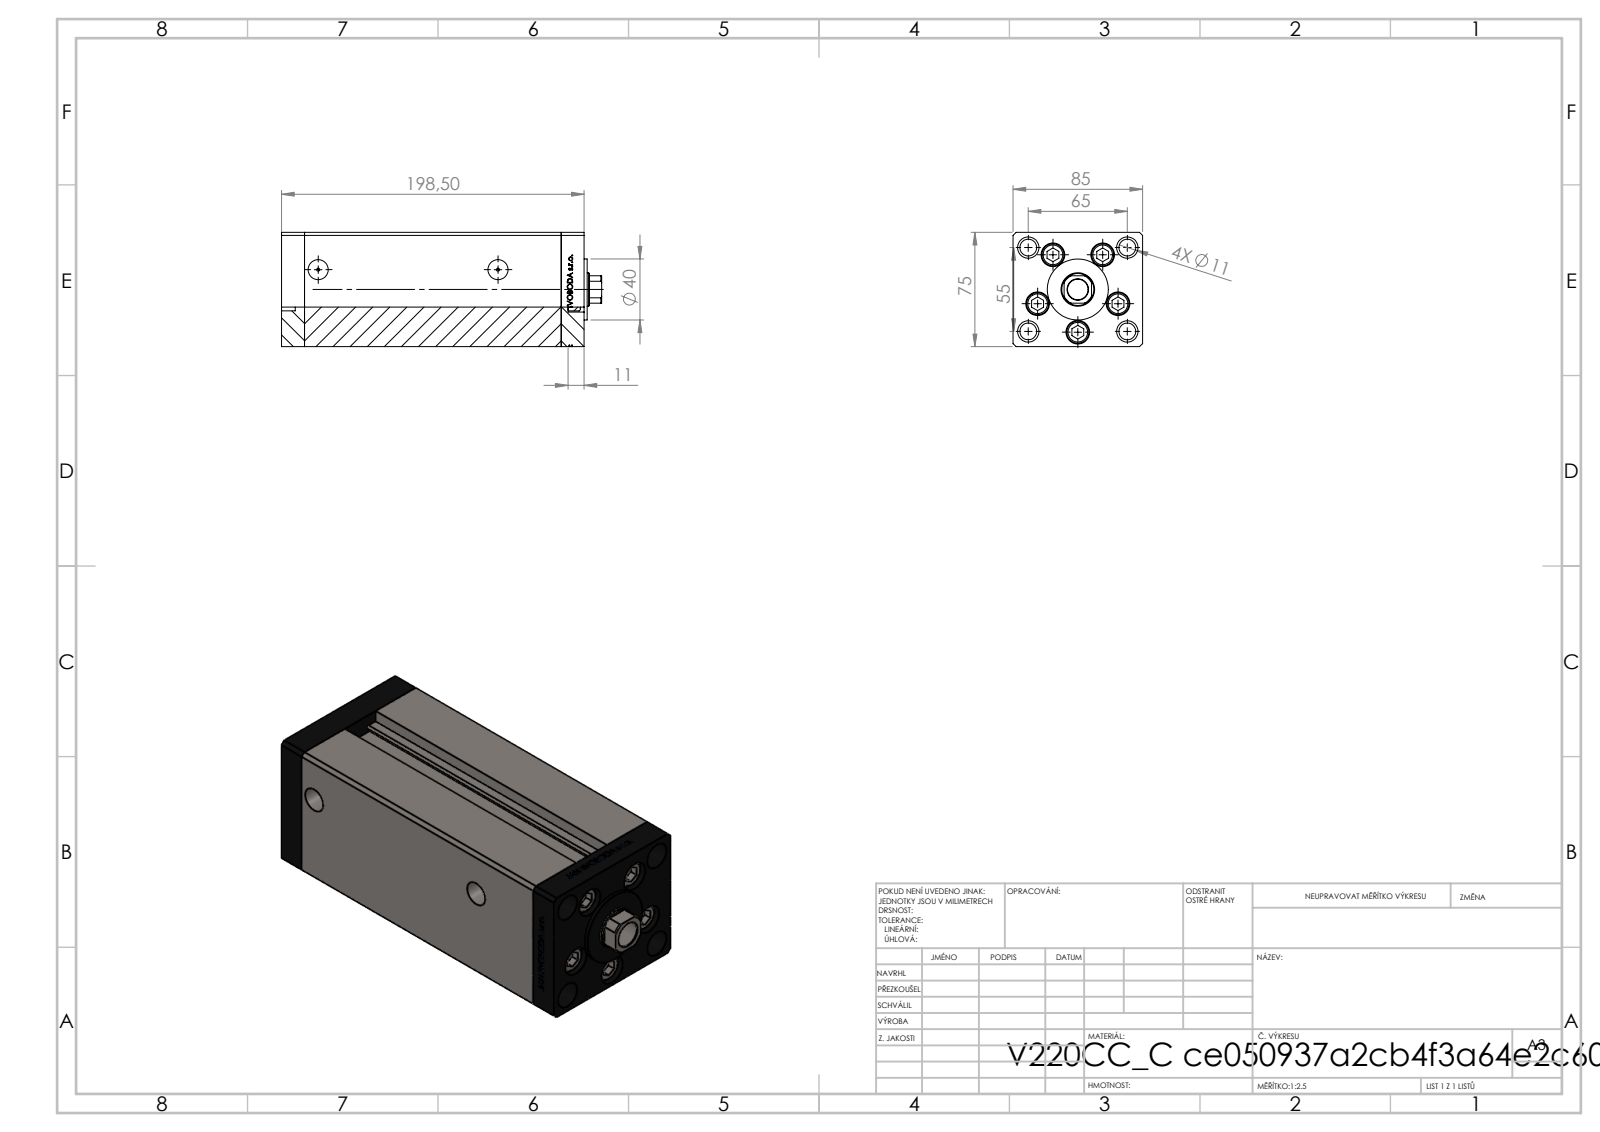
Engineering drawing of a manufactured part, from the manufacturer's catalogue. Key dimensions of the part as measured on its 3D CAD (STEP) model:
Part name (STEP PRODUCT): V220C FRONT; V220C_VC_C; V220C_C MIDDLE; V220C BACK_C (+1 more)
STEP written by: SolidWorks 2019 (CONFIG_CONTROL_DESIGN)
Units: millimetres
Bodies: 13 solids, 1175 faces (546 planar, 167 cylindrical, 462 other)
Overall size (bounding box): 210 × 85 × 75
Volume: 1 045 000 mm³ · Surface area: 194 082 mm²
Round holes (diameter × count): ⌀11 ×9, ⌀15.5 ×5, ⌀10 ×4, ⌀14 ×4, ⌀2 ×2, ⌀13.16 ×2, ⌀13.5 ×1, ⌀14.5 ×1, ⌀22 ×1
Round bosses / shafts (diameter × count): ⌀8 ×5, ⌀14.5 ×4, ⌀40 ×1
Partial cylindrical surfaces — rounded edges, fillets, slot ends (radius × count): R0.93 ×2, R10.5 ×1
Main face-to-face distances: 85, 75, 168.5, 15, 183.5, 10.5, 198.5, 34.25, 68.5, 164.25
Hole centre spacings: 28, 42.57, 16.86, 19.17, 32.33, 32.5, 33.63, 37.33
